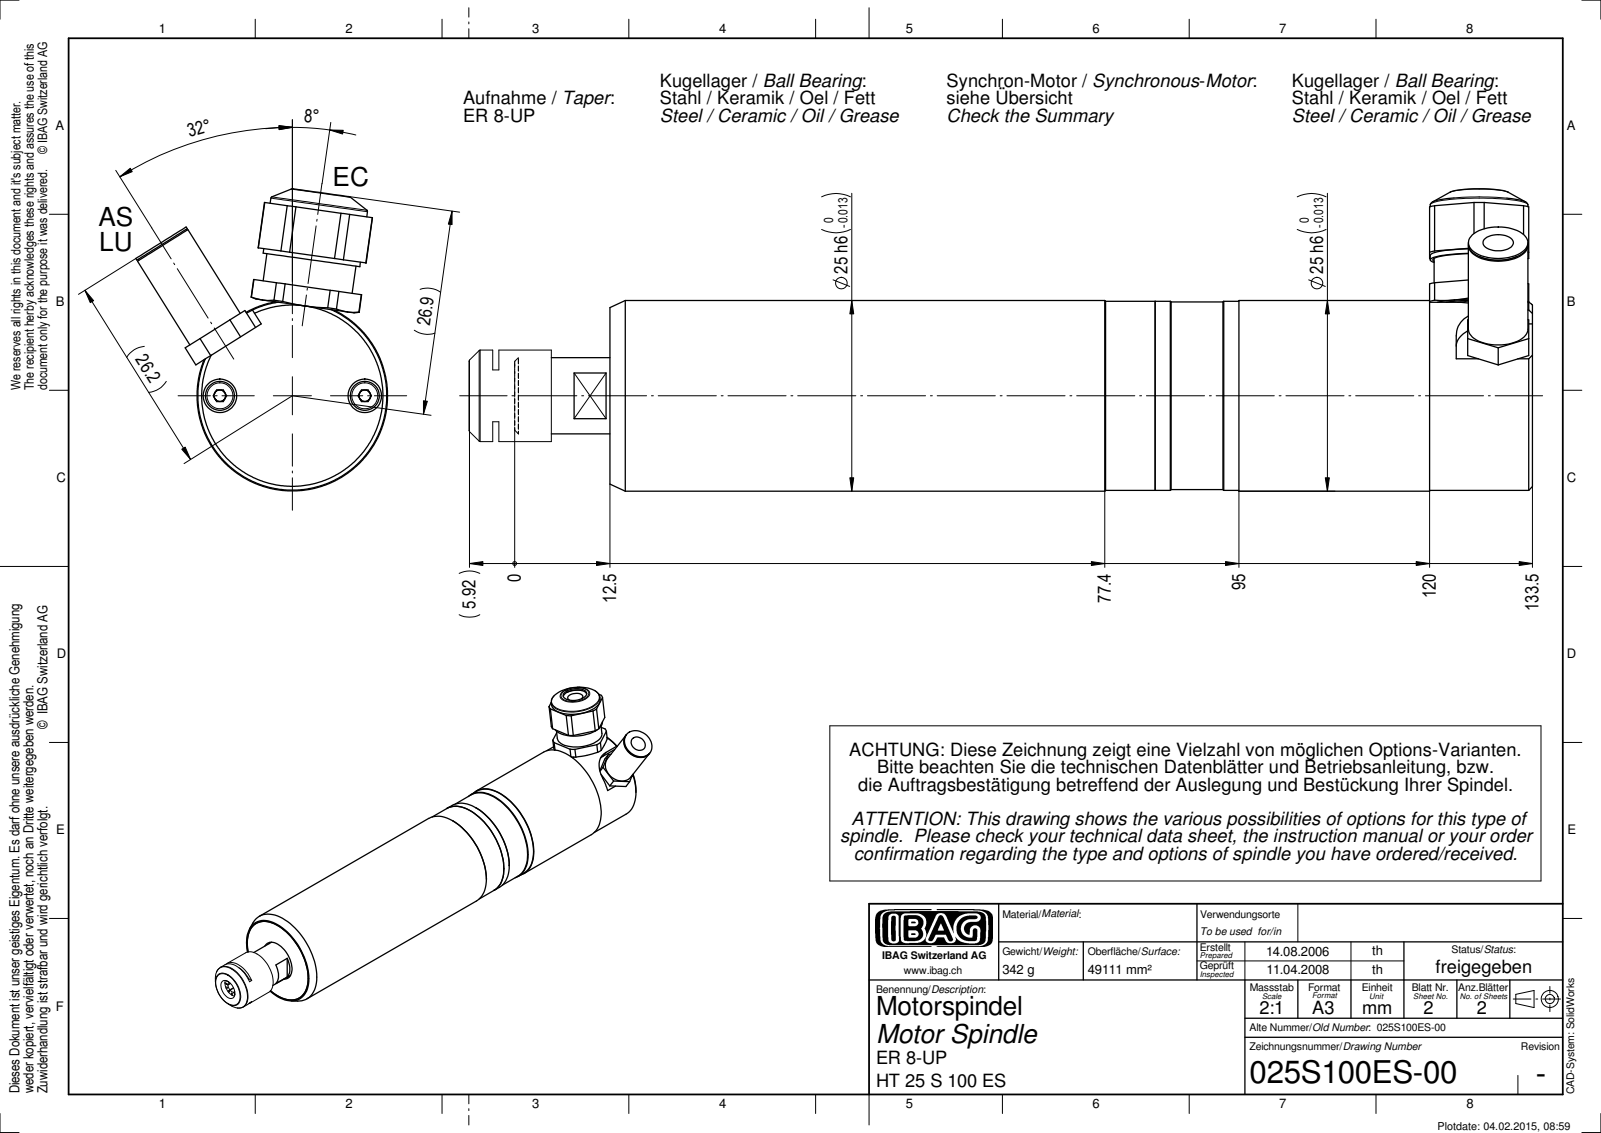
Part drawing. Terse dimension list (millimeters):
name: 025S100ES-00
written by: SolidWorks 2010 (CONFIG_CONTROL_DESIGN)
unit: mm
bodies: 0 solids, 216 faces (95 planar, 72 cylindrical, 49 other)
size: 139.48 × 39.65 × 33.04
holes: 2× ⌀4, 2× ⌀4.4, 1× ⌀3, 1× ⌀5.2, 1× ⌀6.2, 1× ⌀10.6, 1× ⌀22.6
bosses: 2× ⌀3.8, 1× ⌀25, 1× ⌀24.8, 1× ⌀24.6, 1× ⌀12.8, 1× ⌀12, 1× ⌀11.79, 1× ⌀10
rounds: 2× R7.15, 1× R4.25, 1× R5.5
face distances: 121, 1.8, 119.2, 71.5, 69.7, 49.5, 13, 107.5, 105.7, 36
hole spacings: 9.5, 19
